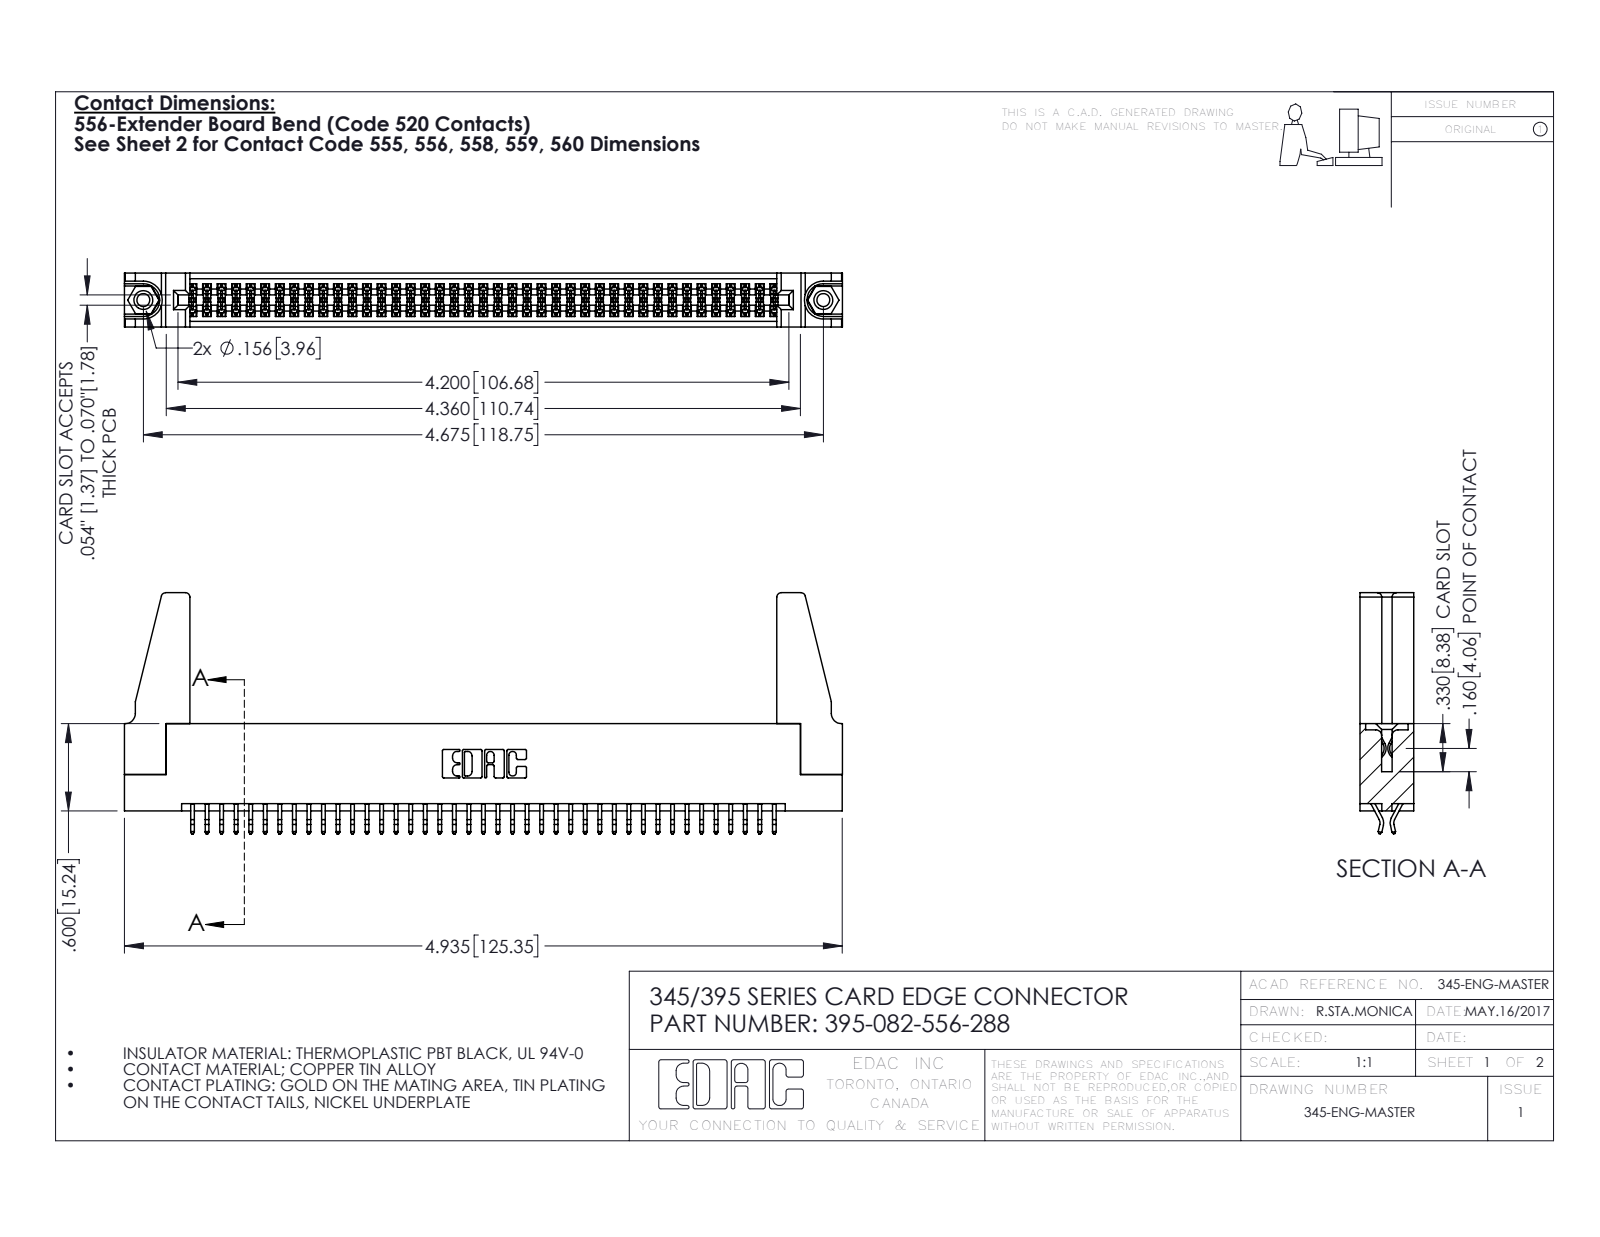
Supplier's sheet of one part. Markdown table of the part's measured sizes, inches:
| quantity | value |
| --- | --- |
| part name | 395-082-556-288; 345-250-001_345-250-001-102; 345-220-078_345-220-088; 345 Part_Flush Mounting Lugs - 0.156 Dia-TH (+1 more) |
| STEP written by | SolidWorks 2016 (CONFIG_CONTROL_DESIGN) |
| units | inches |
| bodies | 87 solids, 4842 faces (3186 planar, 1640 cylindrical, 16 other) |
| overall size | 4.936 × 1.657 × 0.37 |
| volume | 0.941 in³ |
| surface area | 32.57 in² |
| round holes (diameter × count) | 0.089 × 2, 0.125 × 2, 0.156 × 2, 0.064 × 1 |
| round bosses / shafts (diameter × count) | 0.155 × 2 |
| partial cylindrical surfaces (radius × count) | 0.006 × 123, 0.01 × 22, 0.03 × 8, 0.007 × 6, 0.031 × 6, 0.026 × 3, 0.01 × 2, 0.014 × 2 |
| main face-to-face distances | 0.072, 0.298, 0.37, 0.2, 0.025, 0.098, 0.272, 0.225, 0.175, 0.149 |
| hole center spacings | 0.27, 4.439, 4.675 |
